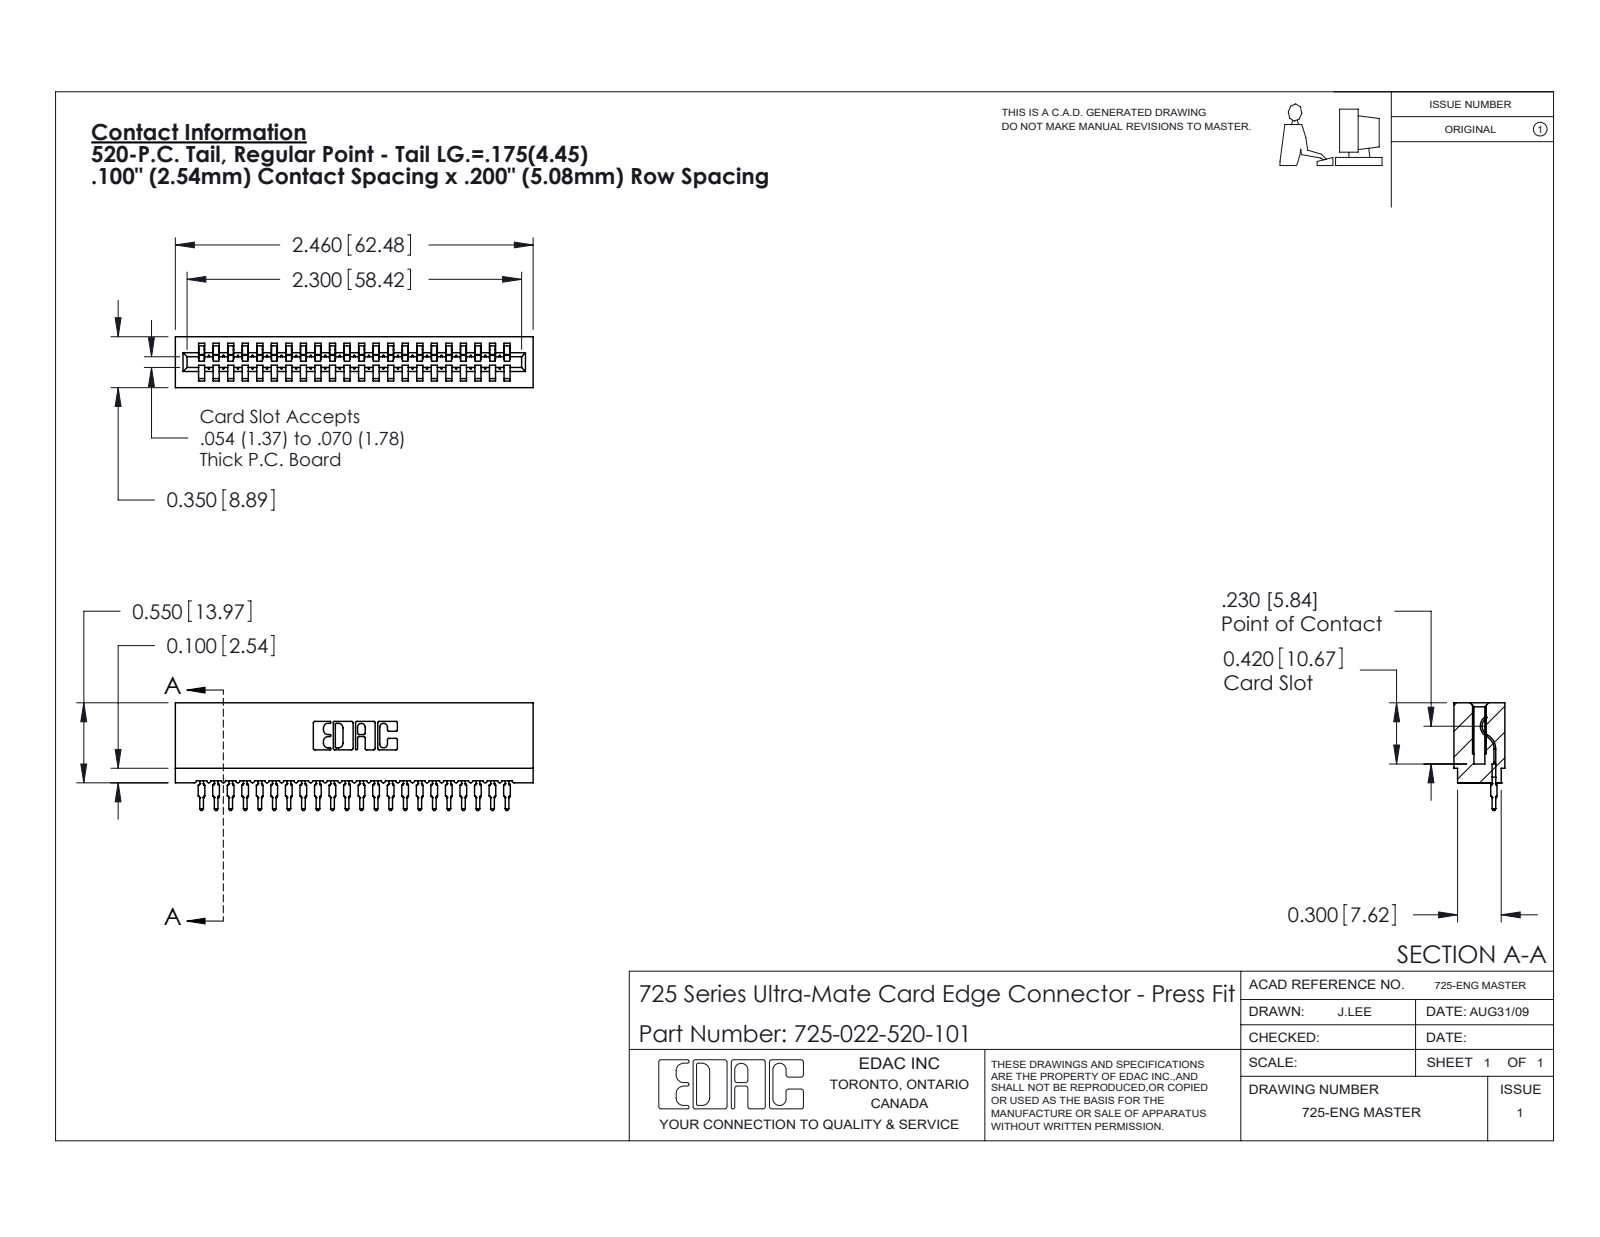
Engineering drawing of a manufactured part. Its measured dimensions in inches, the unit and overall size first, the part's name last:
Units: inches
Overall size (bounding box): 2.46 × 0.741 × 0.35
Partial cylindrical surfaces — rounded edges, fillets, slot ends (radius × count): R0.015 ×44, R0.021 ×44, R0.01 ×22, R0.007 ×6, R0.031 ×6, R0.005 ×4, R0.011 ×4, R0.026 ×3
Main face-to-face distances: 0.1, 0.2, 0.3, 0.35, 0.6, 0.4, 0.7, 0.5, 0.212, 0.138
Volume: 0.294 in³ · Surface area: 13.63 in²
Bodies: 23 solids, 2559 faces (1529 planar, 458 cylindrical, 572 other)
Part name (STEP PRODUCT): 745-292-001_520; 725-022-520-101; 725 Part_Insulator Option - 01
STEP written by: SolidWorks 2020 (CONFIG_CONTROL_DESIGN)
